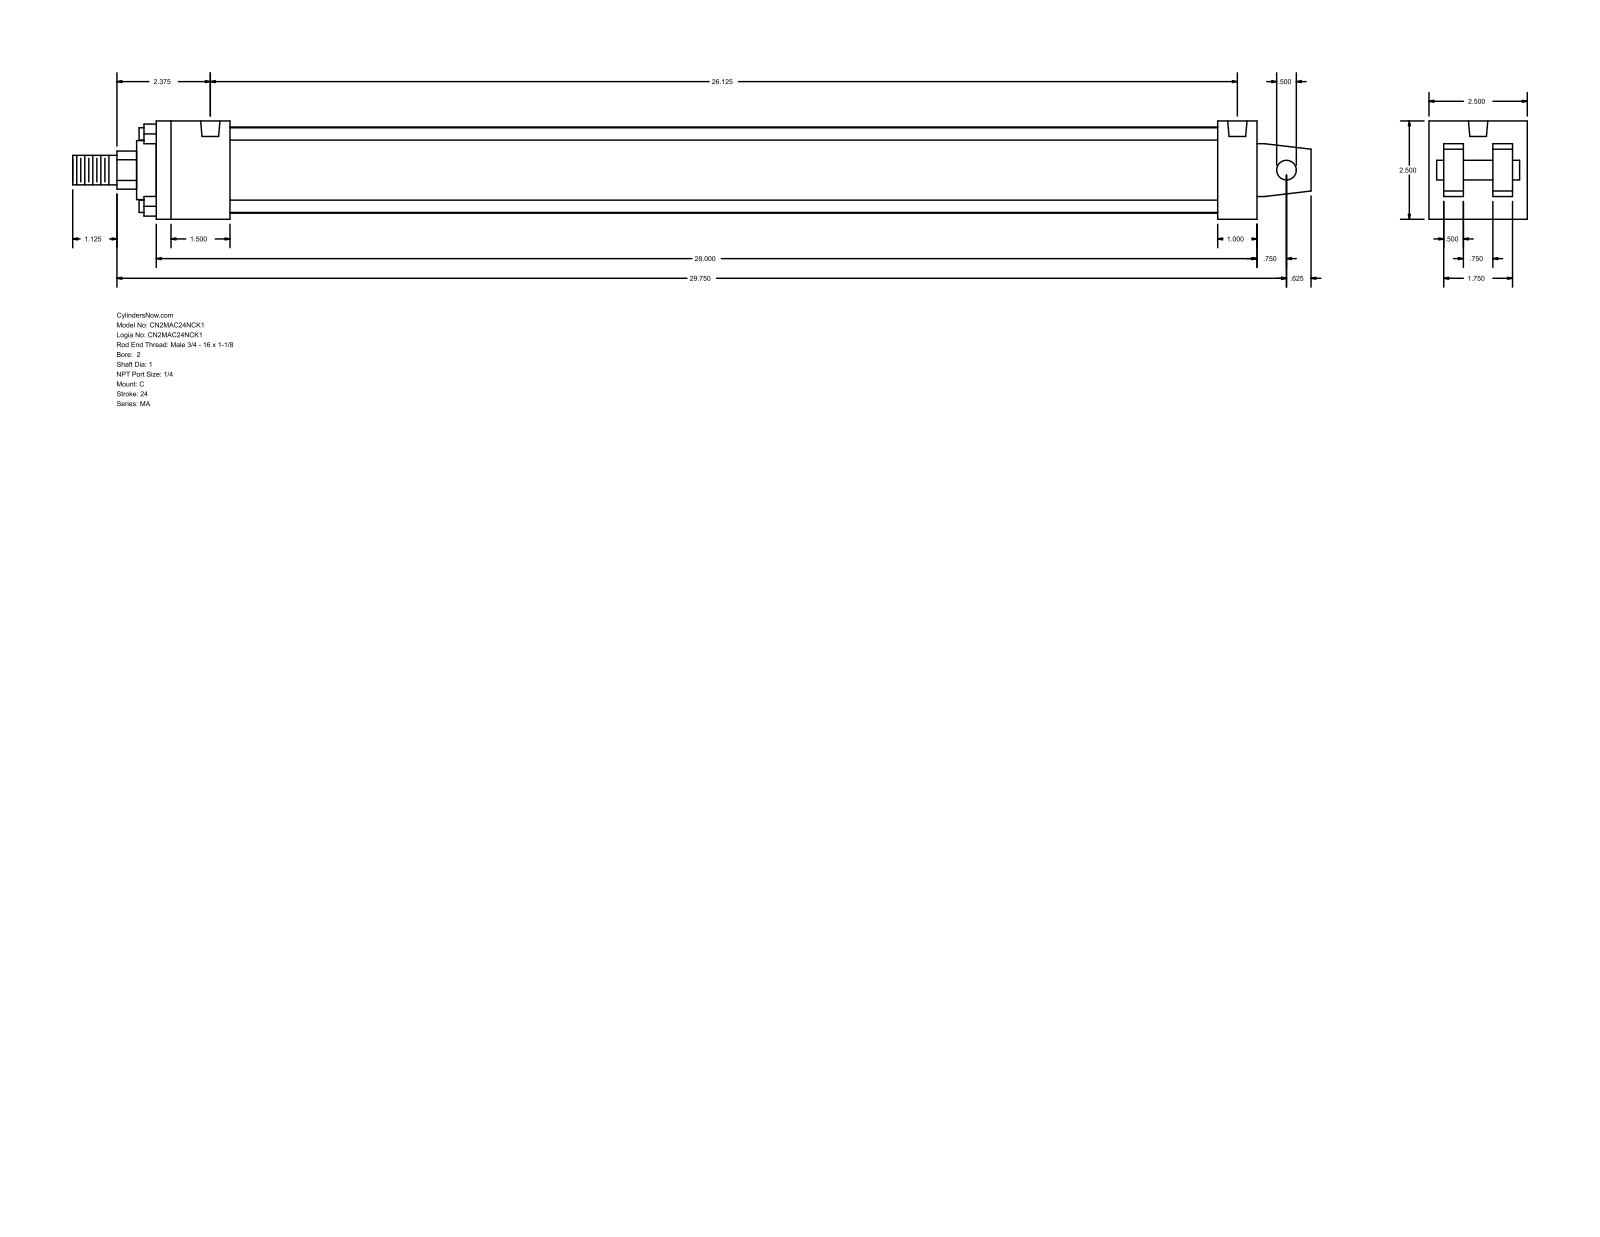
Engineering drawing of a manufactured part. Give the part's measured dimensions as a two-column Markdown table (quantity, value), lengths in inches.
| quantity | value |
| --- | --- |
| part name | MA_C__0200_1 |
| STEP written by | GSSL Pune (CONFIG_CONTROL_DESIGN) |
| units | inches |
| bodies | 0 solids, 103 faces (76 planar, 27 cylindrical, 0 other) |
| overall size | 31.5 × 2.5 × 2.5 |
| round holes (diameter × count) | 0.313 × 4, 0.492 × 2 |
| round bosses / shafts (diameter × count) | 0.313 × 4, 2.19 × 1, 1.5 × 1, 1 × 1, 0.75 × 1, 0.5 × 1 |
| partial cylindrical surfaces (radius × count) | 0.484 × 1 |
| main face-to-face distances | 2.5, 0.5, 28, 0.875, 1.625, 0.375, 2.125, 1.25, 1.875, 1 |
| hole center spacings | 26.125 |
